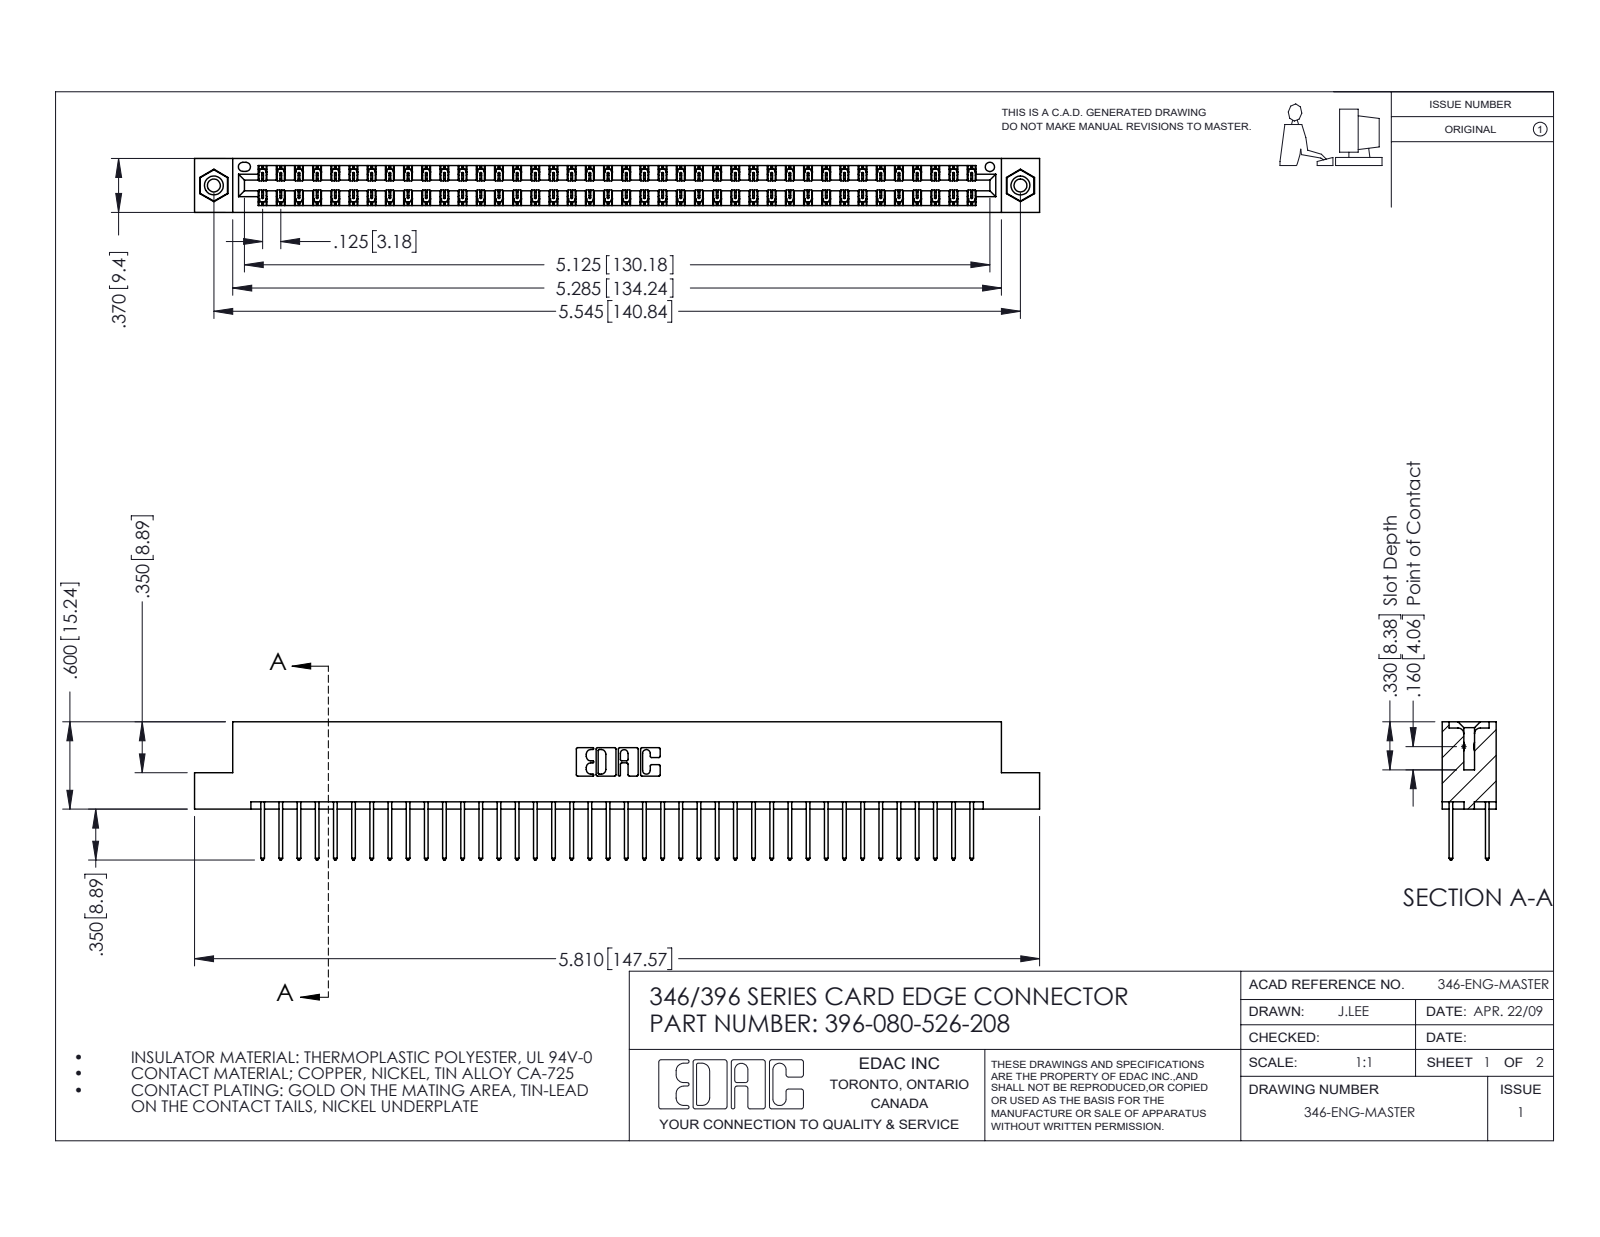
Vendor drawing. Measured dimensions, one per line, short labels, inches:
name: 345-292-001_345-293-126; 345-250-001_345-250-003-102; 346 Part_Flush Mounting Lugs - 0.156 Dia-TI; 396-080-526-208
written by: SolidWorks 2016 (CONFIG_CONTROL_DESIGN)
unit: in
bodies: 83 solids, 4342 faces (2908 planar, 1418 cylindrical, 16 other)
size: 5.81 × 0.95 × 0.37
volume: 0.885 in³; area: 31.78 in²
holes: 2× ⌀0.089, 2× ⌀0.125, 2× ⌀0.156, 1× ⌀0.064
bosses: 2× ⌀0.155
rounds: 120× R0.006, 80× R0.01, 22× R0.01, 6× R0.007, 6× R0.031, 3× R0.026, 2× R0.014, 2× R0.022
face distances: 0.048, 0.322, 0.25, 0.37, 0.072, 0.298, 0.025, 0.275, 0.148, 0.222
hole spacings: 0.246, 5.336, 5.545
